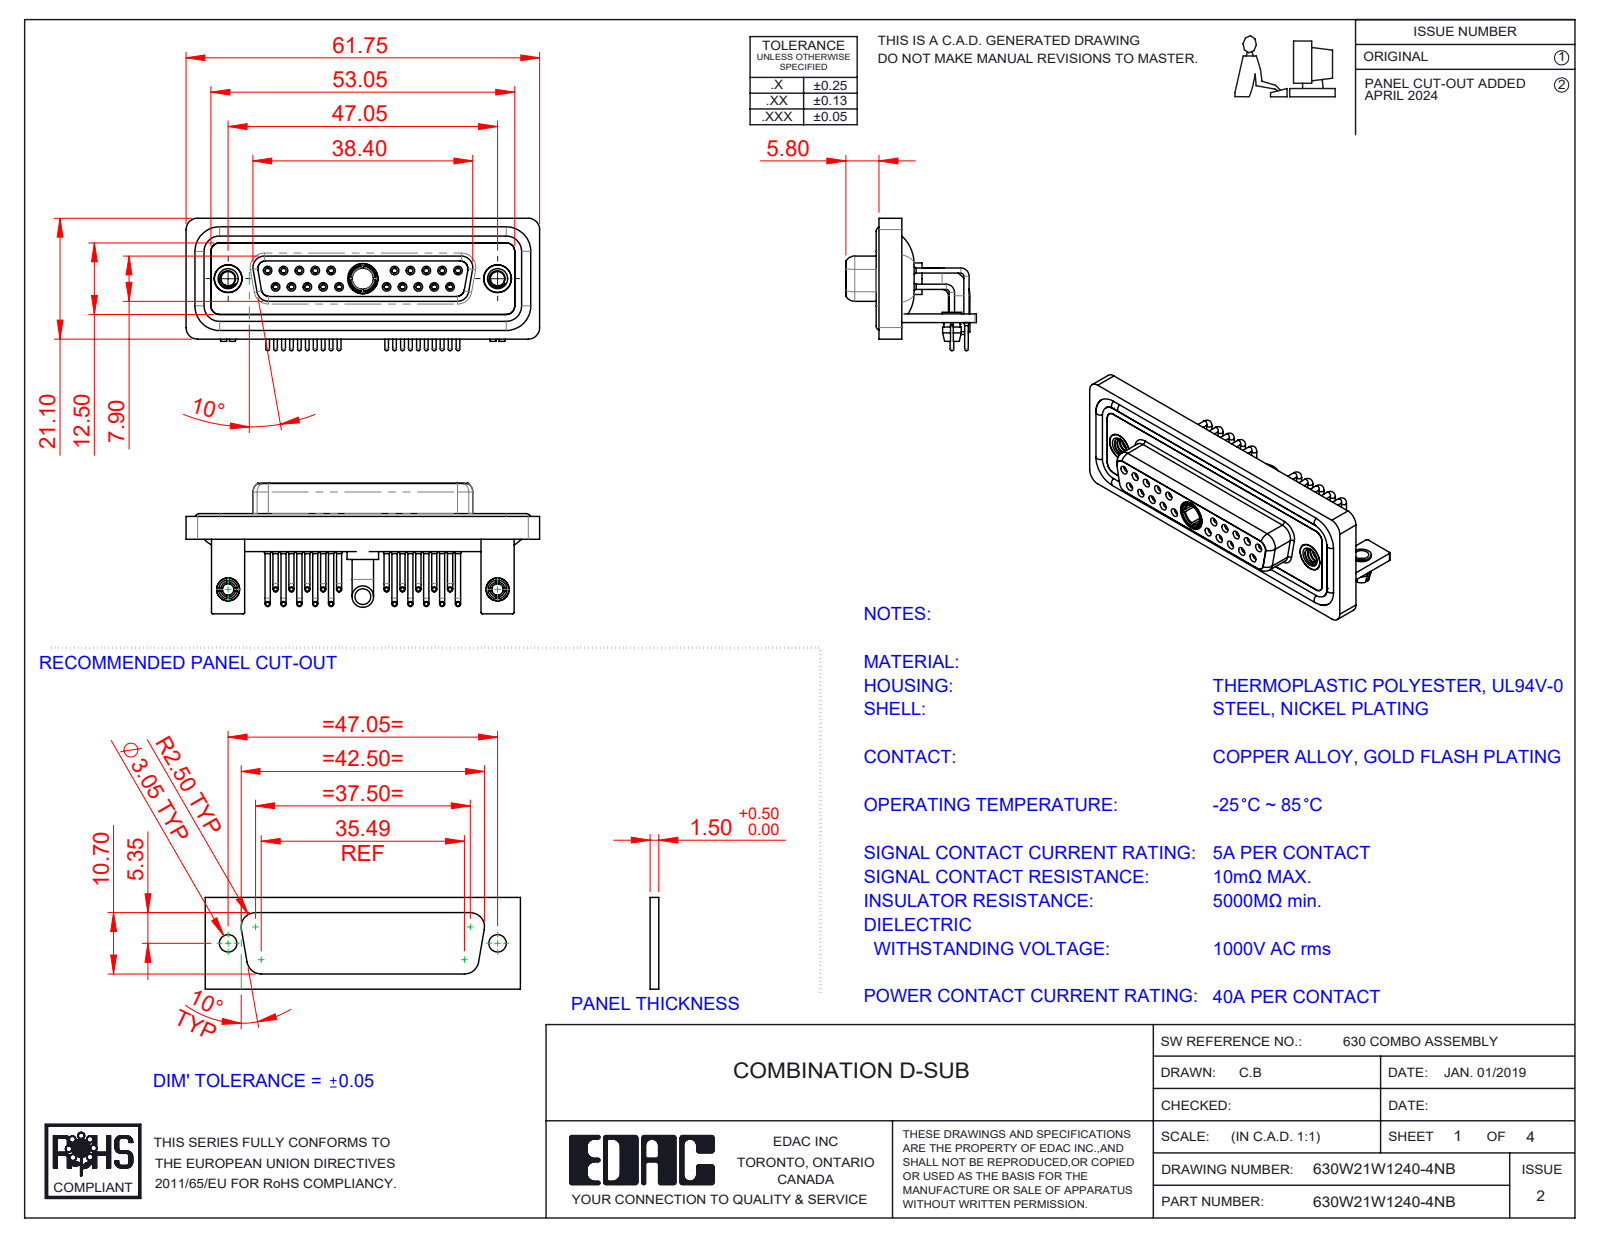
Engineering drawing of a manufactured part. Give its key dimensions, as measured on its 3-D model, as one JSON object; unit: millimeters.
{"part_name": "630Combo Threaded Rivet_A; 630Combo Waterproof Housing_25 Contacts; 630Combo Stabilizer Bracket_50 Contacts; 630W21W1240-4NB (+7 more)", "step_written_by": "SolidWorks 2023 (CONFIG_CONTROL_DESIGN)", "units": "millimeters", "bodies": {"solids": 33, "faces": 1658, "planar": 502, "cylindrical": 727, "other": 429}, "overall_size": [61.75, 23.12, 22.8], "volume_mm3": 8974, "surface_area_mm2": 15773, "round_holes": [[2, 22], [0.9, 20], [1.1, 20], [1.5, 20], [1.6, 10], [1.7, 10], [2.5, 4], [4.85, 3], [3.2, 2], [4, 2], [4.05, 2], [5, 2]], "round_bosses_or_shafts": [[0.9, 20], [0.65, 20], [1.6, 14], [4.95, 2], [4.8, 2], [4, 2], [3.75, 2], [3.4, 2]], "partial_cylinders_radius": [[2, 19], [1.5, 18], [0.25, 16], [1.35, 8], [1.6, 8], [0.5, 5], [0.6, 4], [0.65, 4]], "face_to_face_distances": [0.4, 1.8, 2.9, 3.7, 1.5, 4.1, 1.1, 1.4, 1.6, 2.5], "hole_center_spacings": [3.16, 2.77, 5.54, 8.31, 5.04, 19.39, 20.97, 22.16]}
